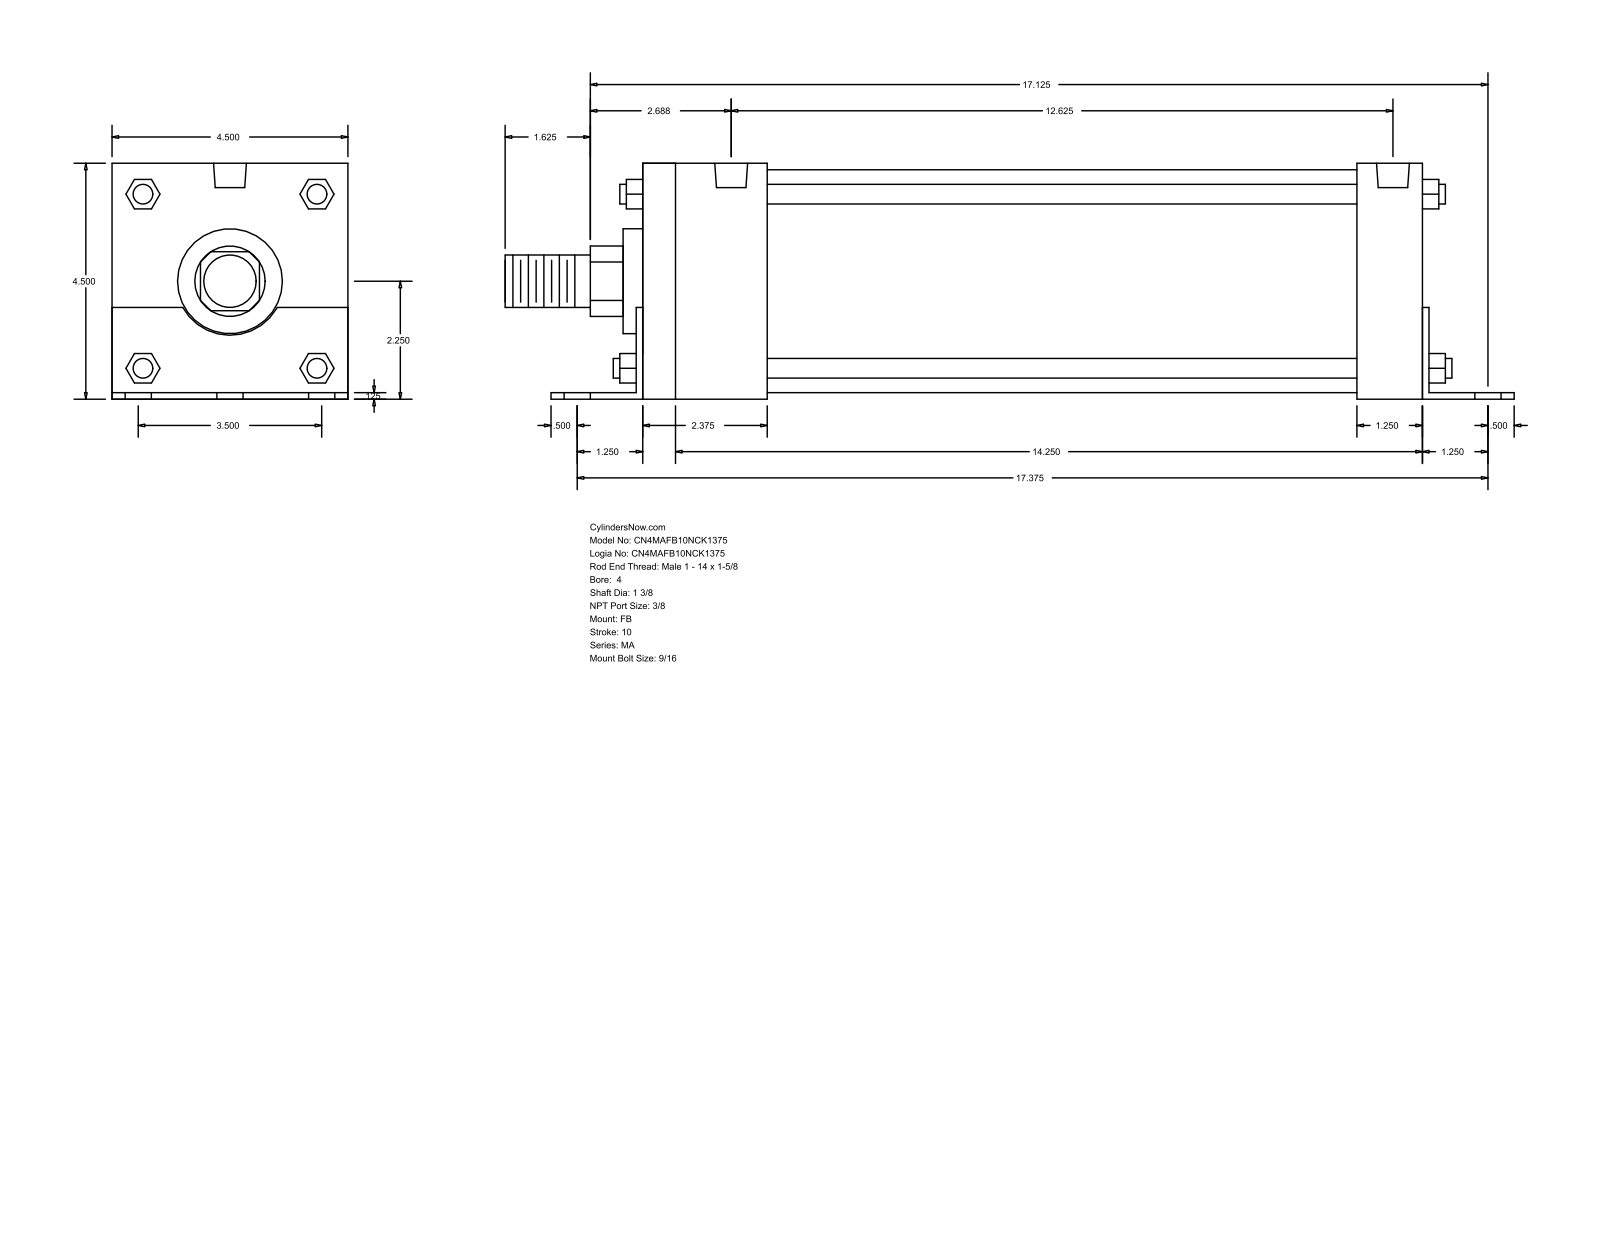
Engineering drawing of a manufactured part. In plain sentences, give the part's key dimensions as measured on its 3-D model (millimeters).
The part is named "MA_FB__0400_1.375". Its 3-D file was written by "GSSL Pune (CONFIG_CONTROL_DESIGN)". It is 0 solids with 140 faces: 105 planar, 35 cylindrical and 0 other. Overall it measures 488.95 by 114.35 by 114.3 millimeters. Round holes: 6 of diameter 14.29, 4 of diameter 11.11, 2 of diameter 15.93. Round bosses or shafts: 4 of diameter 9.53, 1 of diameter 107.95, 1 of diameter 50.8, 1 of diameter 34.92, 1 of diameter 25.4. Partial cylindrical surfaces (rounded edges, fillets, slot ends): 1 of radius 17.06, 1 of radius 26.16. The main face-to-face distances are 114.3, 3.17, 114.35, 3.12, 111.18, 381, 377.83, 384.17, 31.75, 349.25. The hole center spacings are 44.45, 443.56, 441.33, 64, 67.5, 86.85, 88.9, 90.98.
